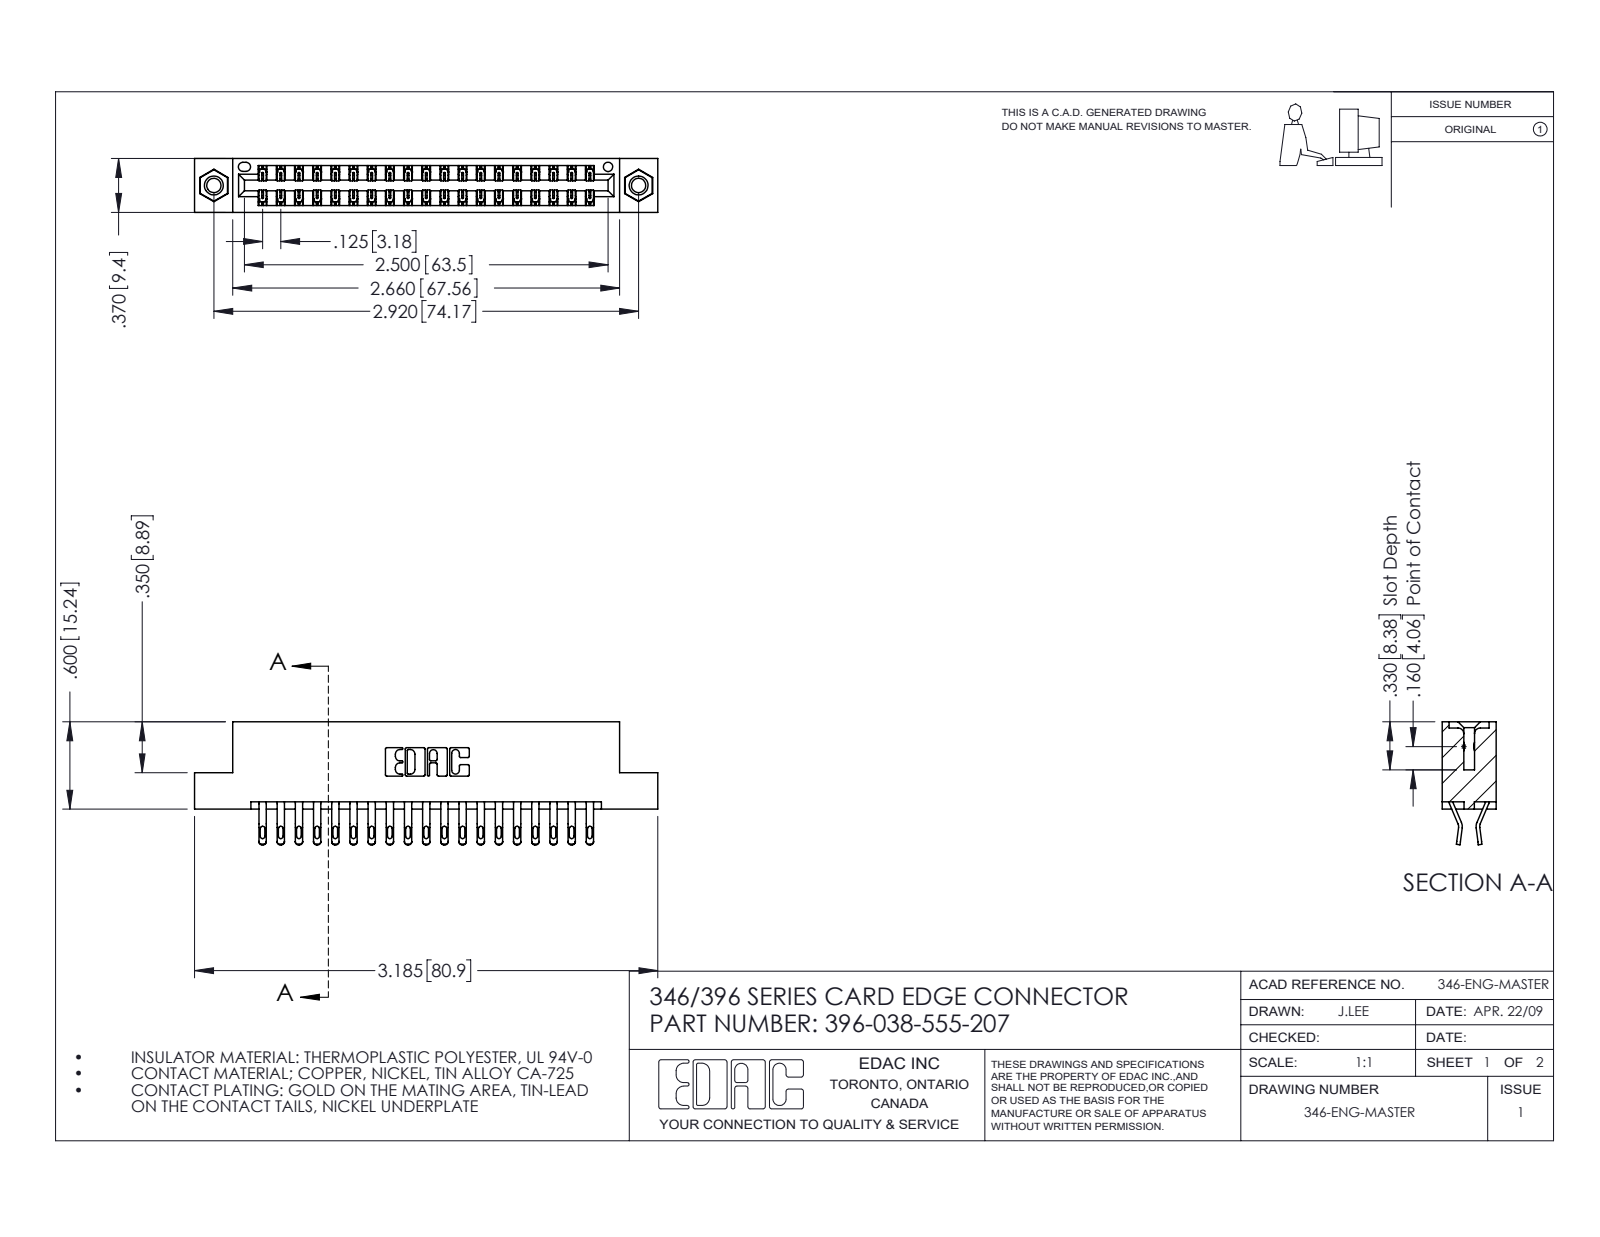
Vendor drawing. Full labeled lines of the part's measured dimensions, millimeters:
Part name (STEP PRODUCT): 346 Part_Flush Mounting Lugs - 0.156 Dia-TI; 396-038-555-207; 345-250-001_345-250-005-103; 345-292-001_555 Tail
STEP written by: SolidWorks 2016 (CONFIG_CONTROL_DESIGN)
Units: millimetres
Bodies: 41 solids, 2386 faces (1362 planar, 1008 cylindrical, 16 other)
Overall size (bounding box): 80.9 × 21.5 × 9.4
Volume: 7 800 mm³ · Surface area: 10 790 mm²
Round holes (diameter × count): ⌀2.5 ×2, ⌀3.2 ×2, ⌀4 ×2, ⌀1.6 ×1
Round bosses / shafts (diameter × count): ⌀3.9 ×2
Partial cylindrical surfaces — rounded edges, fillets, slot ends (radius × count): R0.4 ×76, R0.5 ×76, R0.2 ×57, R0.3 ×22, R0.2 ×6, R0.8 ×6, R0.7 ×3, R0.3 ×2
Main face-to-face distances: 1.2, 8.2, 6.4, 9.4, 0.6, 1.8, 7.6, 7, 3.8, 5.6
Hole centre spacings: 6.2, 68.9, 74.2
